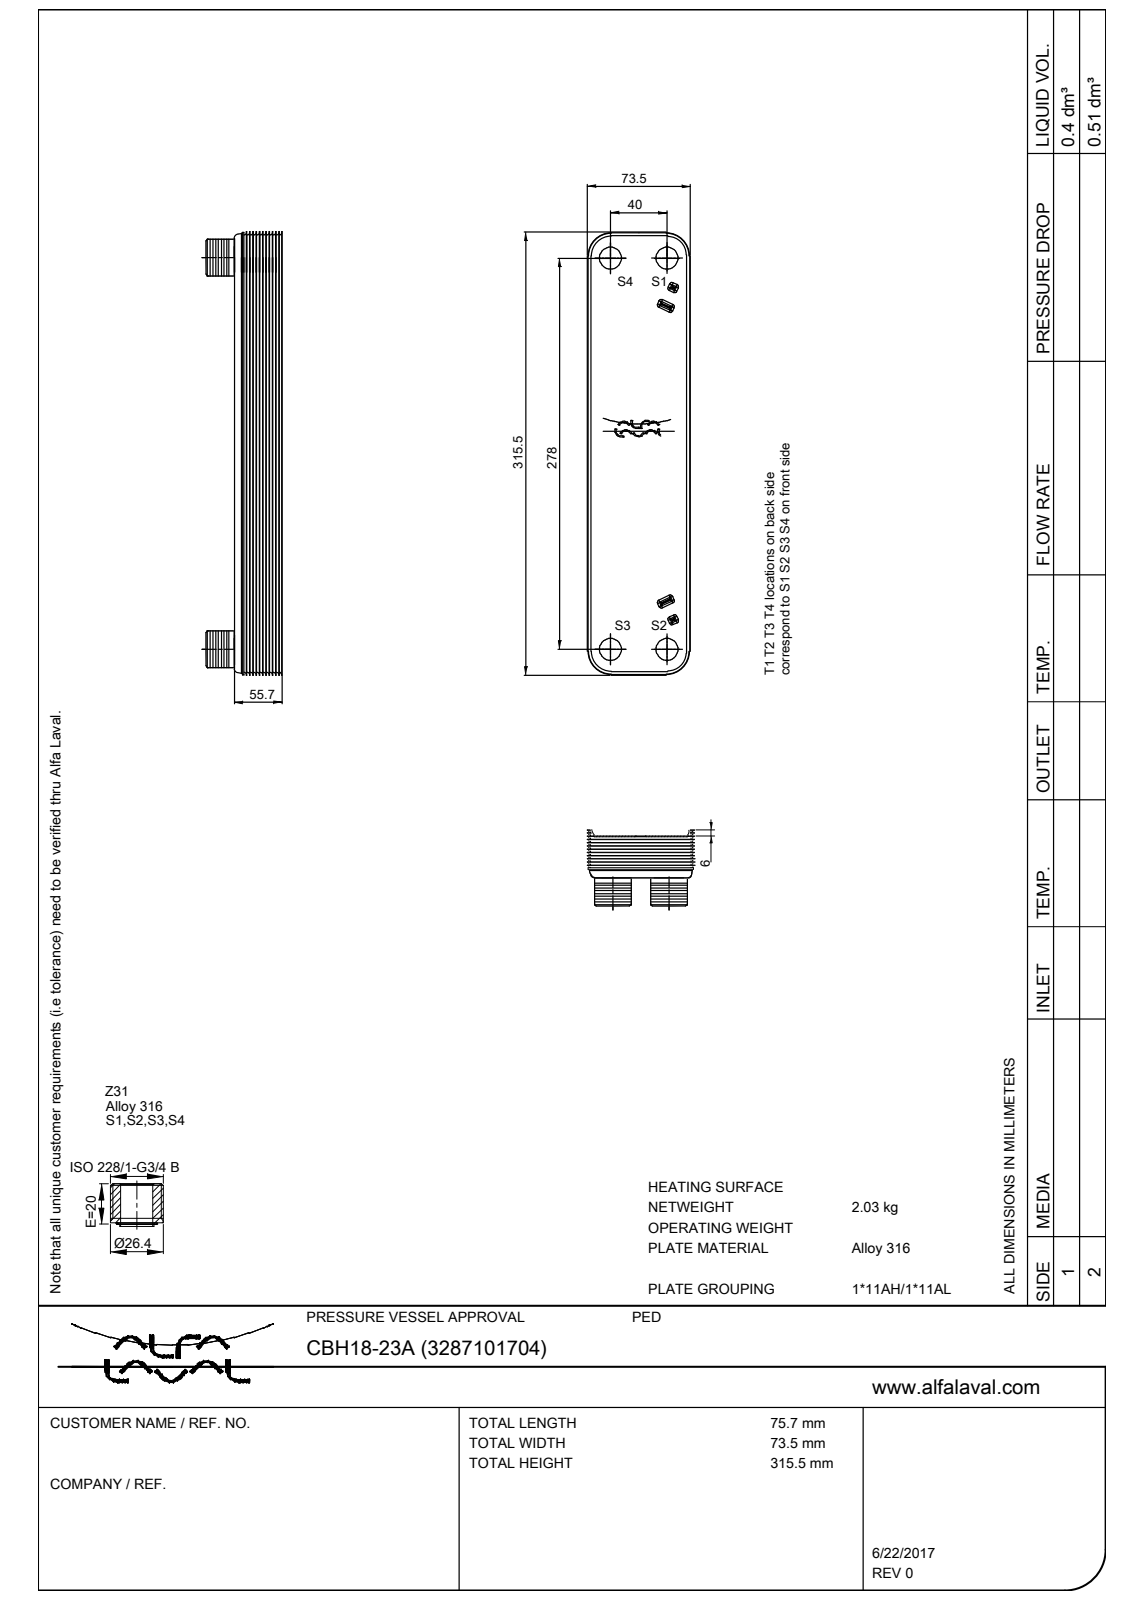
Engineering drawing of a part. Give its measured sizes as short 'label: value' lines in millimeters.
name: CBH18_CH_23H; CBH18_FP_S1S2S3S4_16; CBH18_PP; Z31 (+1 more)
written by: PRO/ENGINEER BY PARAMETRIC TECHNOLOGY CORPORATION, 2007390 (CONFIG_CONTROL_DESIGN)
unit: mm
bodies: 7 solids, 480 faces (128 planar, 144 cylindrical, 208 other)
size: 319 × 77.7 × 77.5
volume: 1 249 000 mm³; area: 221 685 mm²
holes: 4× ⌀16, 4× ⌀16.75, 4× ⌀20.5
bosses: 4× ⌀26.44, 4× ⌀18
rounds: 18× R1, 16× R0.4, 16× R0.7, 16× R1.4, 16× R1.7, 4× R0.5, 4× R1.5, 4× R20
face distances: 1, 51, 50, 52, 77.5, 7.14, 1.04, 1.15, 52.15, 6.94
hole spacings: 40, 278, 280.86
